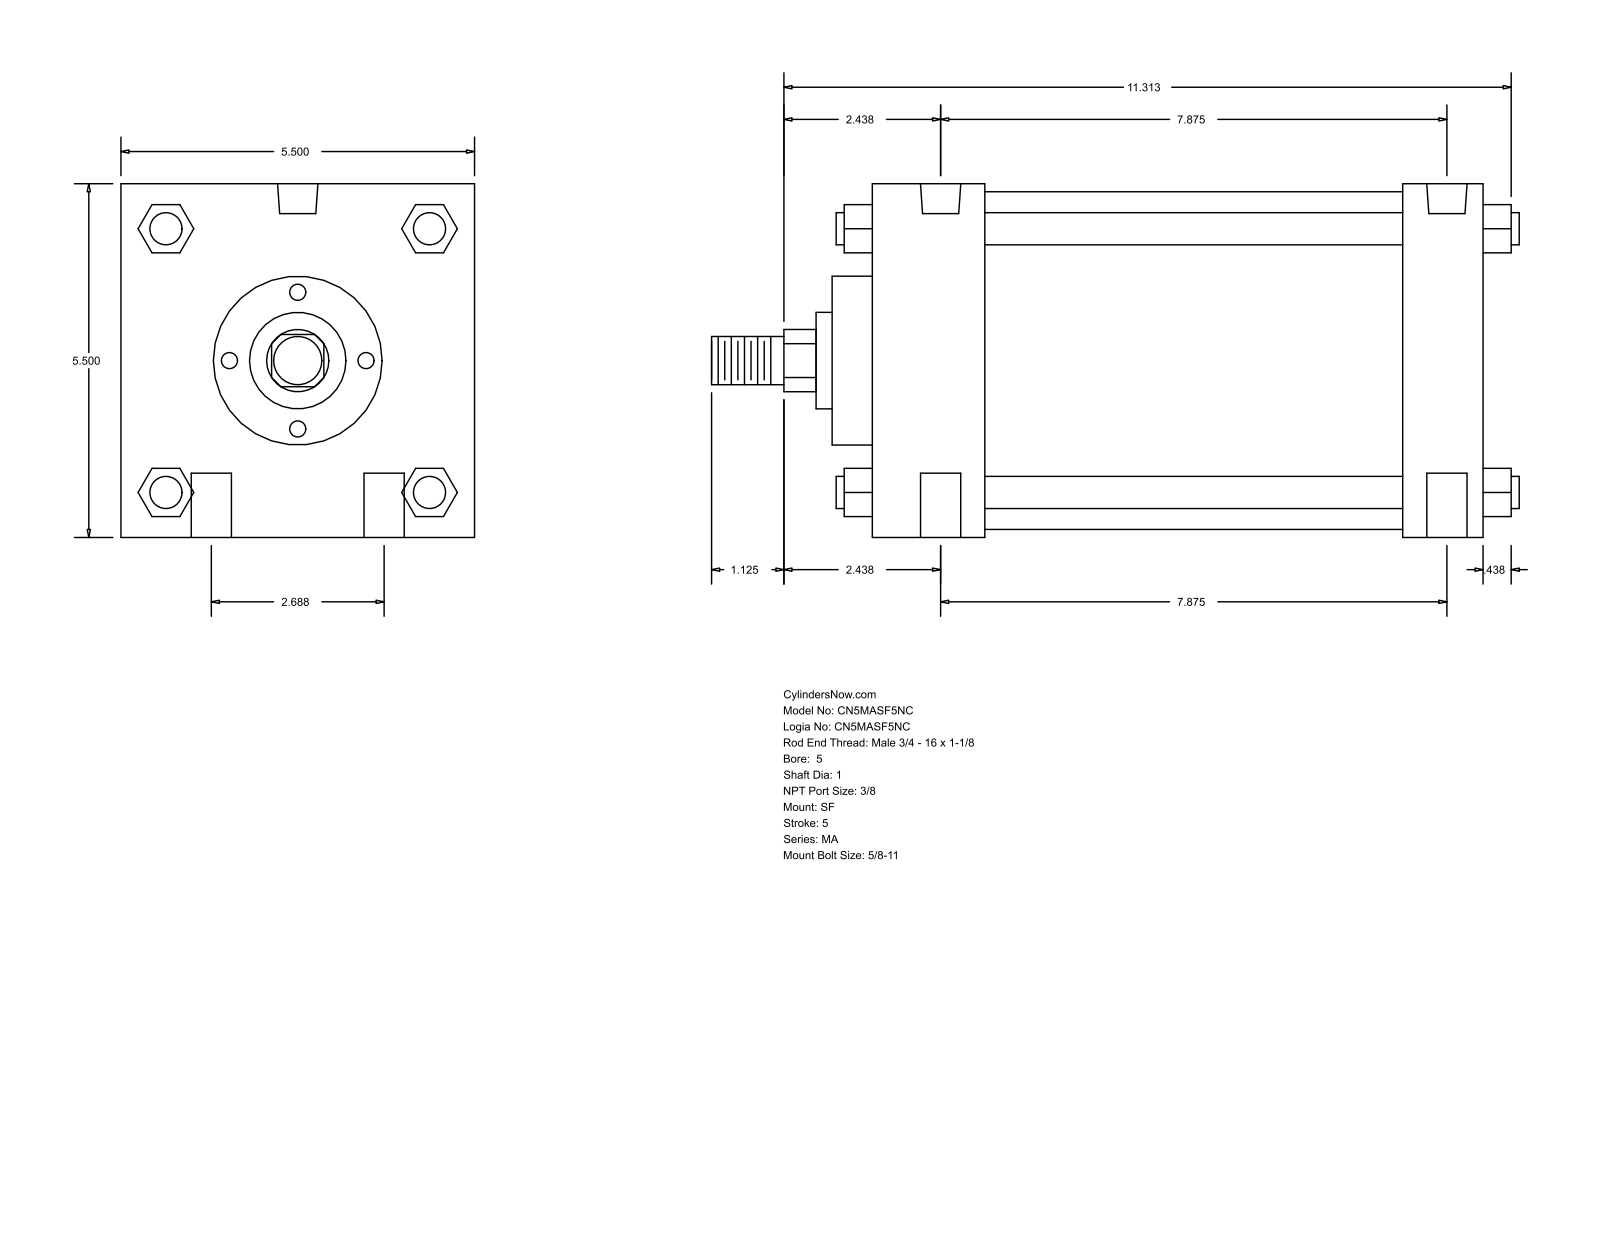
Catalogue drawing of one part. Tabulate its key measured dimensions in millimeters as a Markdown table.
| quantity | value |
| --- | --- |
| part name | MA_SF__0500_1 |
| STEP written by | GSSL Pune (CONFIG_CONTROL_DESIGN) |
| units | millimeters |
| bodies | 0 solids, 126 faces (95 planar, 31 cylindrical, 0 other) |
| overall size | 319.09 × 139.7 × 139.7 |
| round holes (diameter × count) | 15.88 × 4, 11.11 × 2, 15.93 × 2 |
| round bosses / shafts (diameter × count) | 12.7 × 4, 133.35 × 1, 66.67 × 1, 38.1 × 1, 25.4 × 1, 19.05 × 1 |
| partial cylindrical surfaces (radius × count) | 12.29 × 1 |
| main face-to-face distances | 139.7, 241.31, 44.46, 209.55, 165.09, 196.85, 31.76, 15.87, 60.33, 225.42 |
| hole center spacings | 34.13, 202.92, 200.03, 68.26, 211.36, 190.51 |
